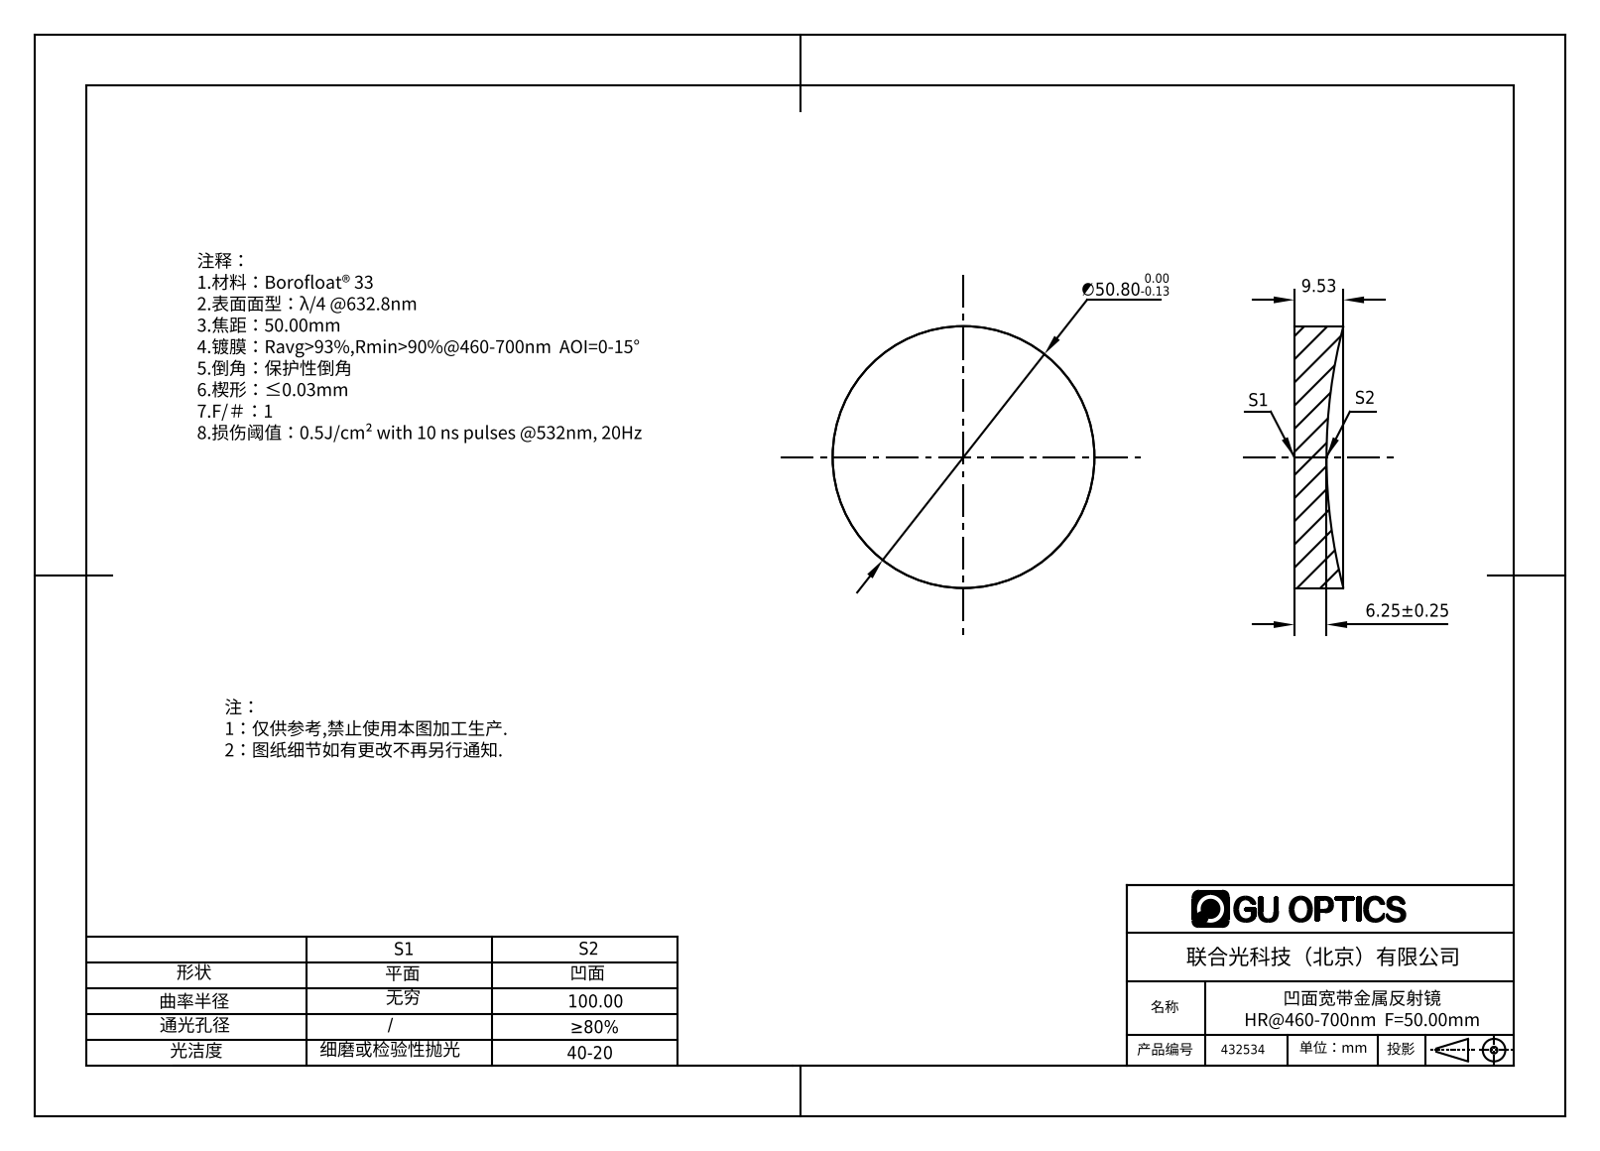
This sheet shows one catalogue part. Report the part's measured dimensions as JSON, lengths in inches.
{"part_name": "432530", "step_written_by": "SolidWorks 2016 (AUTOMOTIVE_DESIGN)", "units": "inches", "bodies": {"solids": 1, "faces": 5, "planar": 1, "cylindrical": 2, "other": 2}, "overall_size": [2, 2, 0.375], "volume_in3": 0.975, "surface_area_in2": 8.692, "round_bosses_or_shafts": [[2, 1]]}
